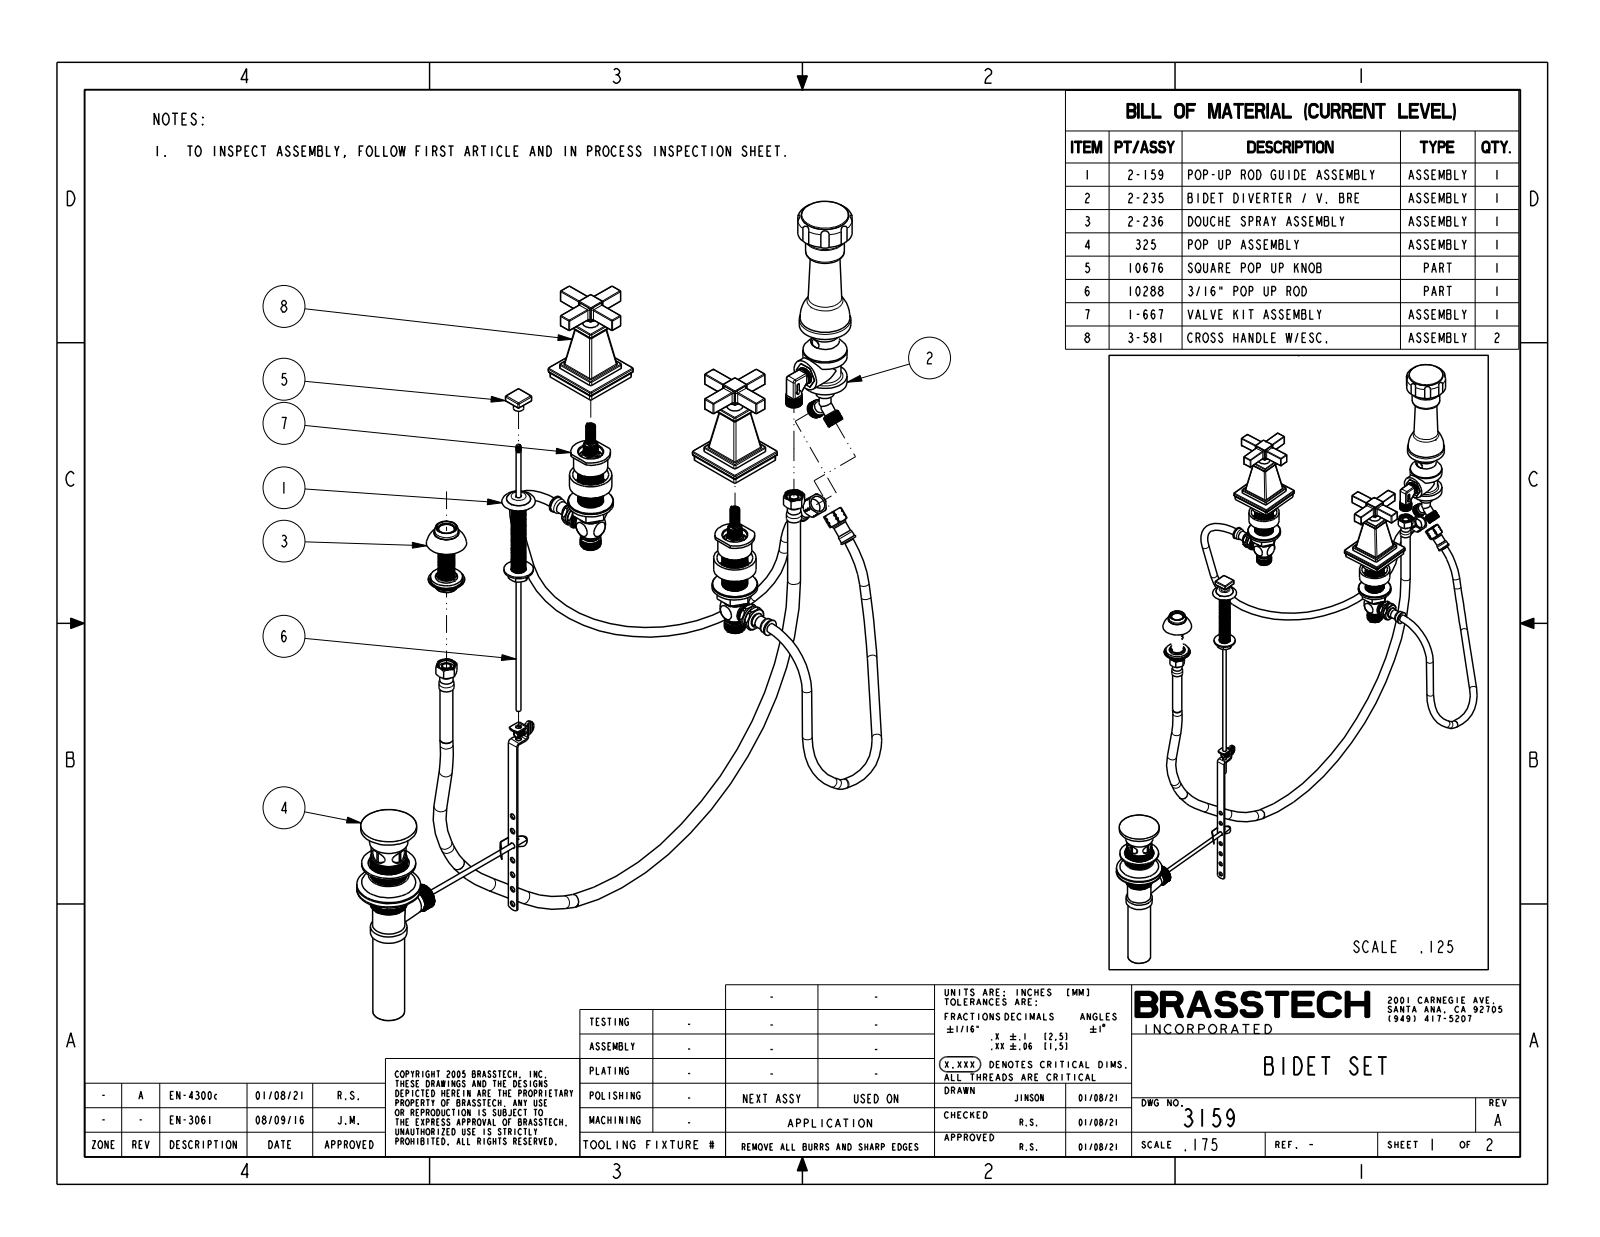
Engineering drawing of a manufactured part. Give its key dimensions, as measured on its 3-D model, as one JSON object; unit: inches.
{"part_name": "3159", "step_written_by": "CREO PARAMETRIC BY PTC INC, 2018400 (CONFIG_CONTROL_DESIGN)", "units": "inches", "bodies": {"solids": 5, "faces": 739, "planar": 161, "cylindrical": 300, "other": 278}, "overall_size": [22.855, 10.875, 5.353], "volume_in3": 26.35, "surface_area_in2": 122.5, "round_holes": [[0.625, 1], [0.792, 1], [0.94, 1]], "round_bosses_or_shafts": [[0.625, 2], [0.506, 2], [2.025, 1], [1.52, 1], [0.925, 1], [0.775, 1], [0.4, 1]], "partial_cylinders_radius": [[0.03, 96], [0.06, 68], [0.04, 12], [0.09, 12], [0.21, 8], [0.23, 8], [0.357, 1], [1.077, 1]], "face_to_face_distances": [0.5, 0.41, 8, 7.88, 3.035, 2.625, 3.535, 3.125, 0.895, 1.395]}
